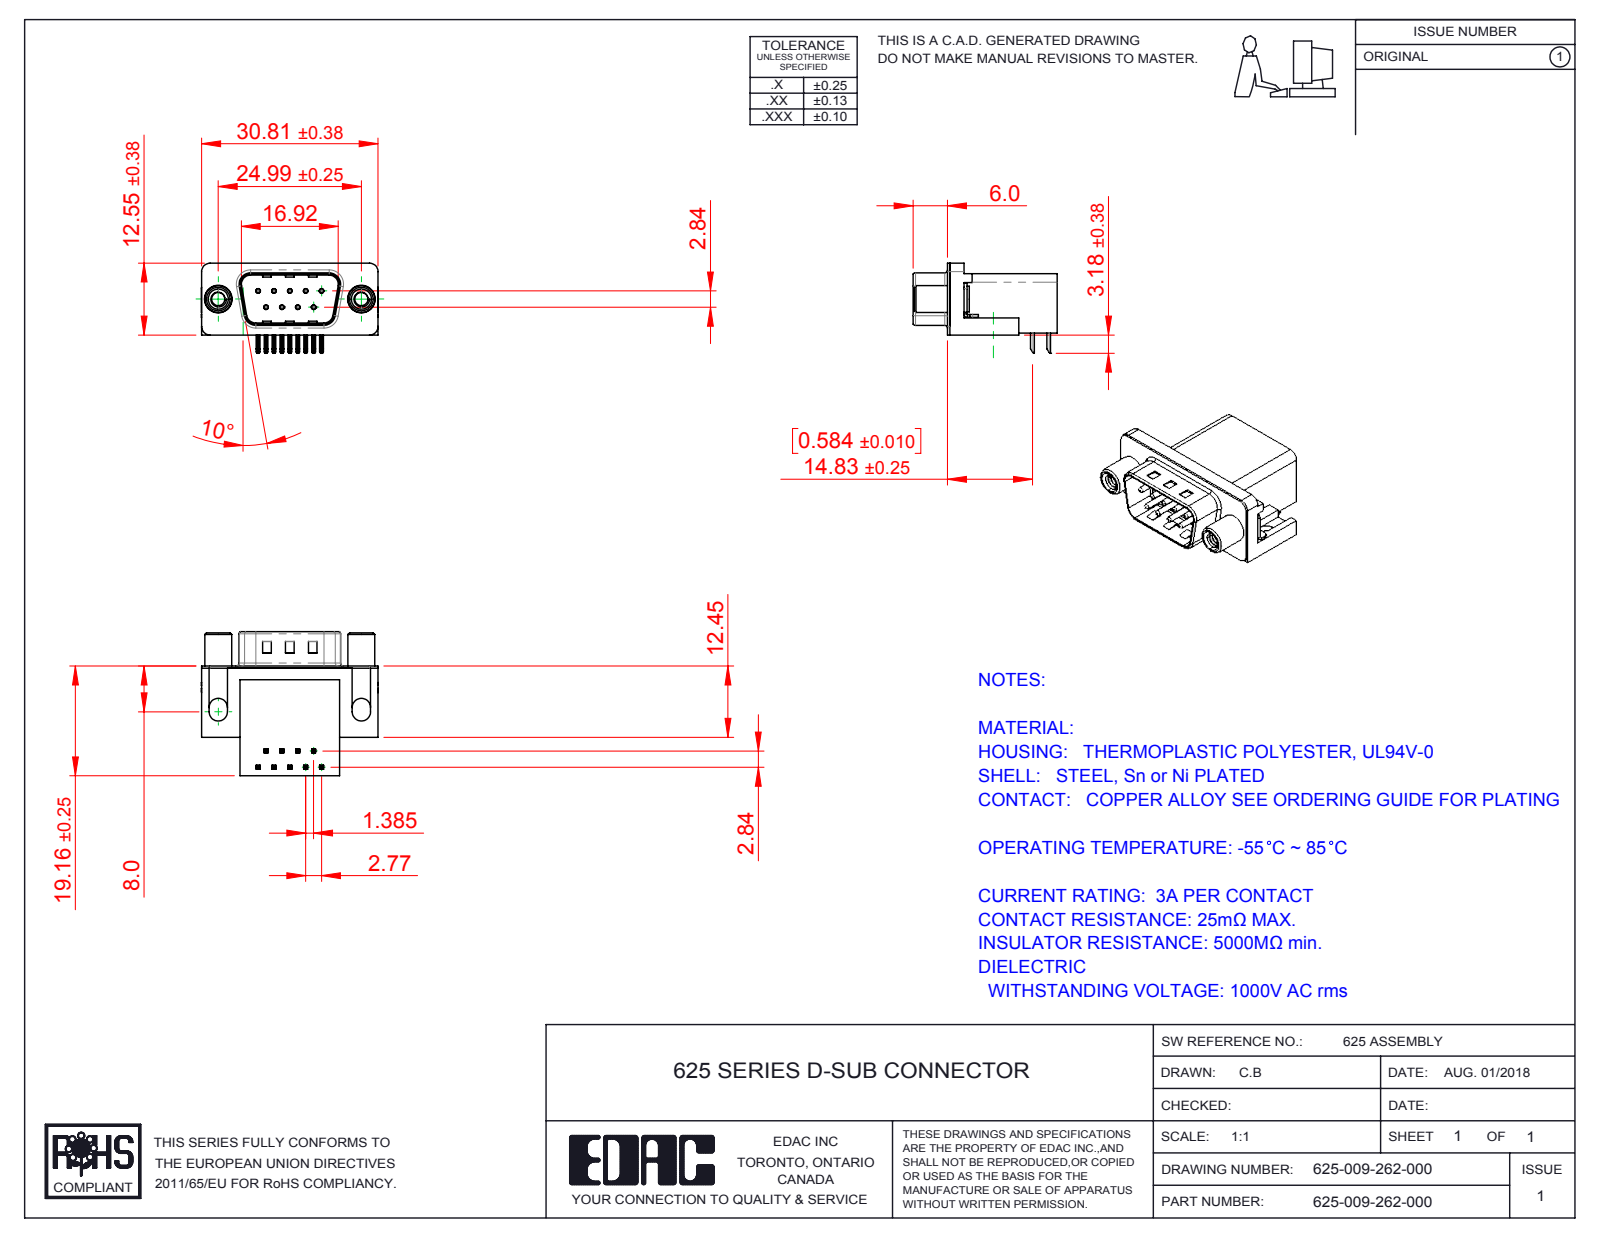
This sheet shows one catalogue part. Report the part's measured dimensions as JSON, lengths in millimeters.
{"part_name": "625-009-262-000; 625 Housing_9 Socket; 625 Shell_9 Socket; 625 Non Board Mount (+3 more)", "step_written_by": "SolidWorks 2016 (CONFIG_CONTROL_DESIGN)", "units": "millimeters", "bodies": {"solids": 15, "faces": 985, "planar": 567, "cylindrical": 321, "other": 97}, "overall_size": [30.89, 25.16, 15.73], "volume_mm3": 4538, "surface_area_mm2": 5016, "round_holes": [[0.35, 9], [0.8, 9], [2.3, 2], [3.1, 2], [4, 2], [4.8, 2], [5, 2]], "round_bosses_or_shafts": [[0.75, 9], [4.9, 2], [4.7, 2], [4.5, 2], [3.85, 2]], "partial_cylinders_radius": [[0.25, 36], [0.12, 18], [1, 16], [0.5, 9], [1.5, 8], [1.6, 8], [0.9, 4], [2, 4]], "face_to_face_distances": [0.4, 10.34, 18.76, 19.16, 16.26, 2.5, 2.9, 0.35, 10.69, 6.7], "hole_center_spacings": [3.16, 2.77, 5.54, 5.03, 5.04, 8.31, 7.48, 7.49]}
